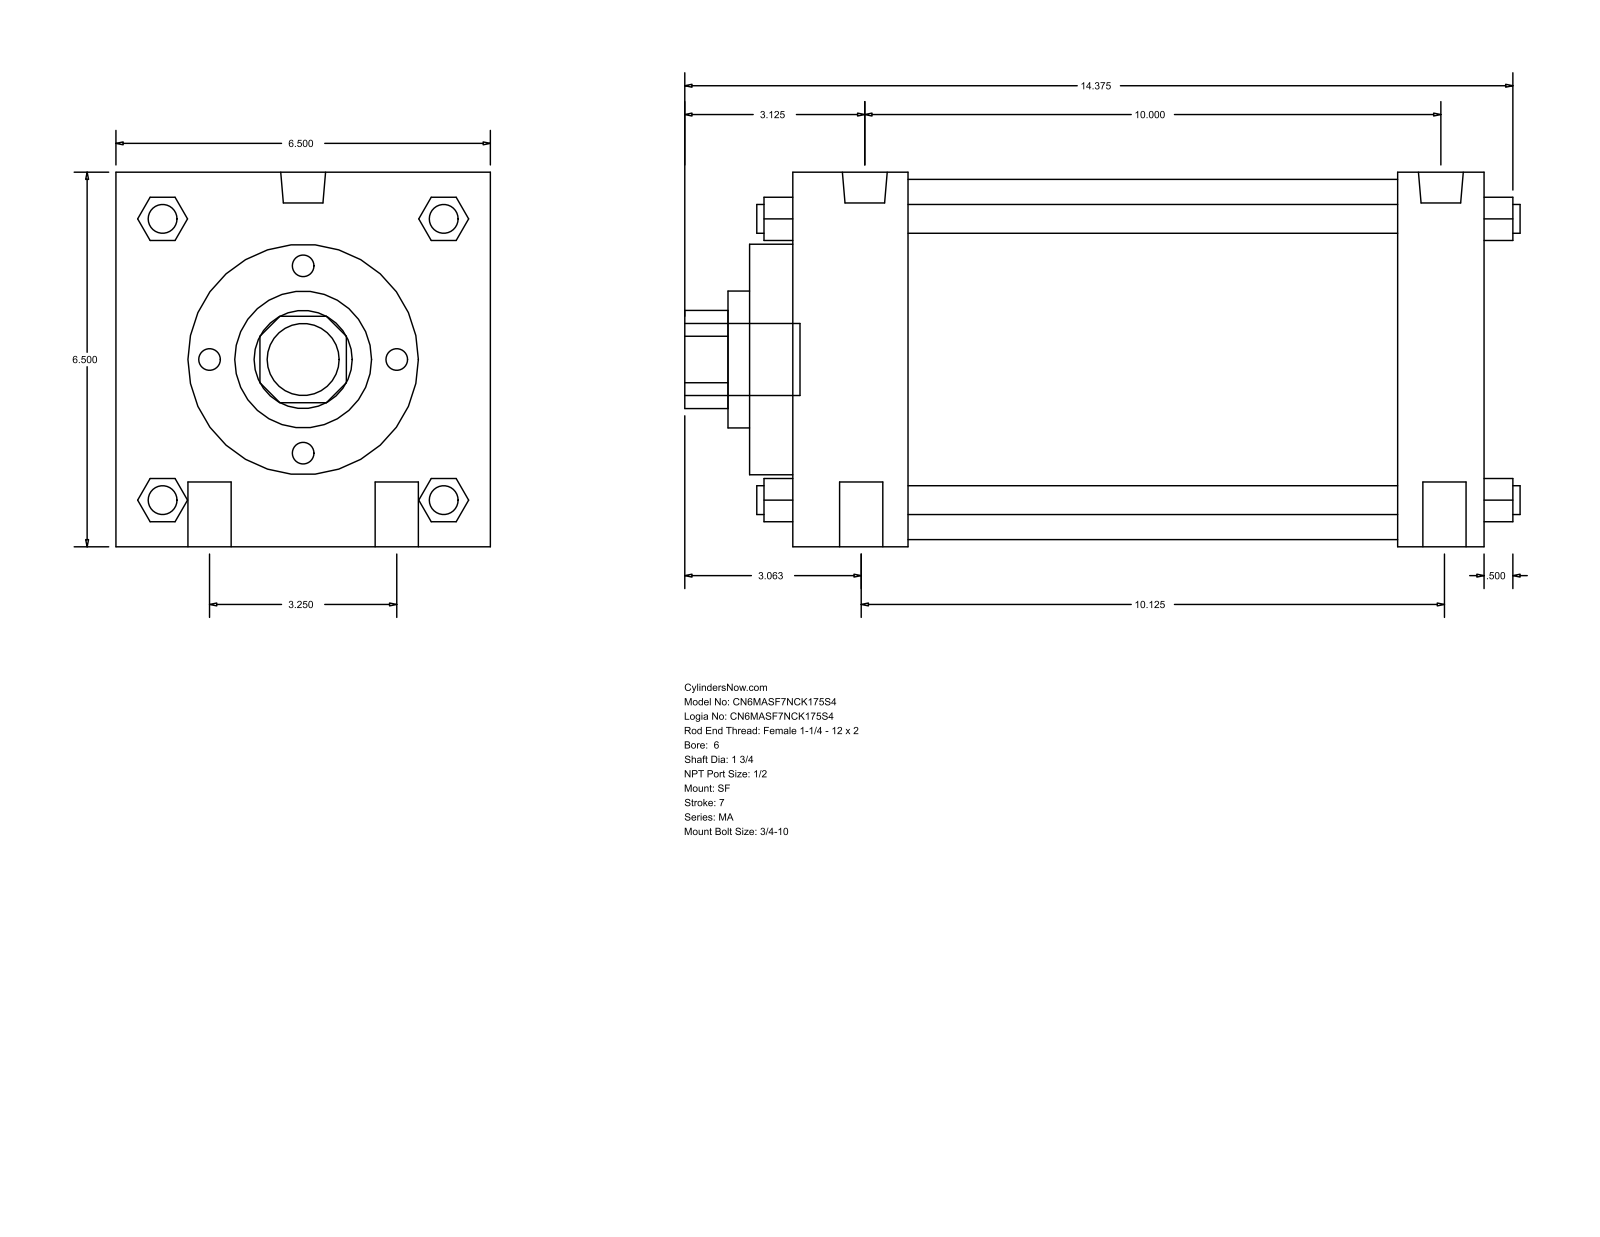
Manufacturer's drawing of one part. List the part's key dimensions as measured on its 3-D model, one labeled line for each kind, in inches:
Part name (STEP PRODUCT): MA_SF__0600_1.75
STEP written by: GSSL Pune (CONFIG_CONTROL_DESIGN)
Units: inches
Bodies: 0 solids, 126 faces (95 planar, 31 cylindrical, 0 other)
Overall size (bounding box): 14.5 × 6.5 × 6.5
Round holes (diameter × count): ⌀1.75 ×1, ⌀2.375 ×1, ⌀4 ×1, ⌀6.25 ×1
Round bosses / shafts (diameter × count): ⌀0.75 ×4, ⌀0.5 ×4, ⌀0.778 ×2, ⌀0.687 ×2, ⌀1.25 ×1
Partial cylindrical surfaces — rounded edges, fillets, slot ends (radius × count): R0.852 ×1
Main face-to-face distances: 6.5, 12, 0.75, 2, 10.5, 1.5, 8.5, 10, 2.75, 11.25
